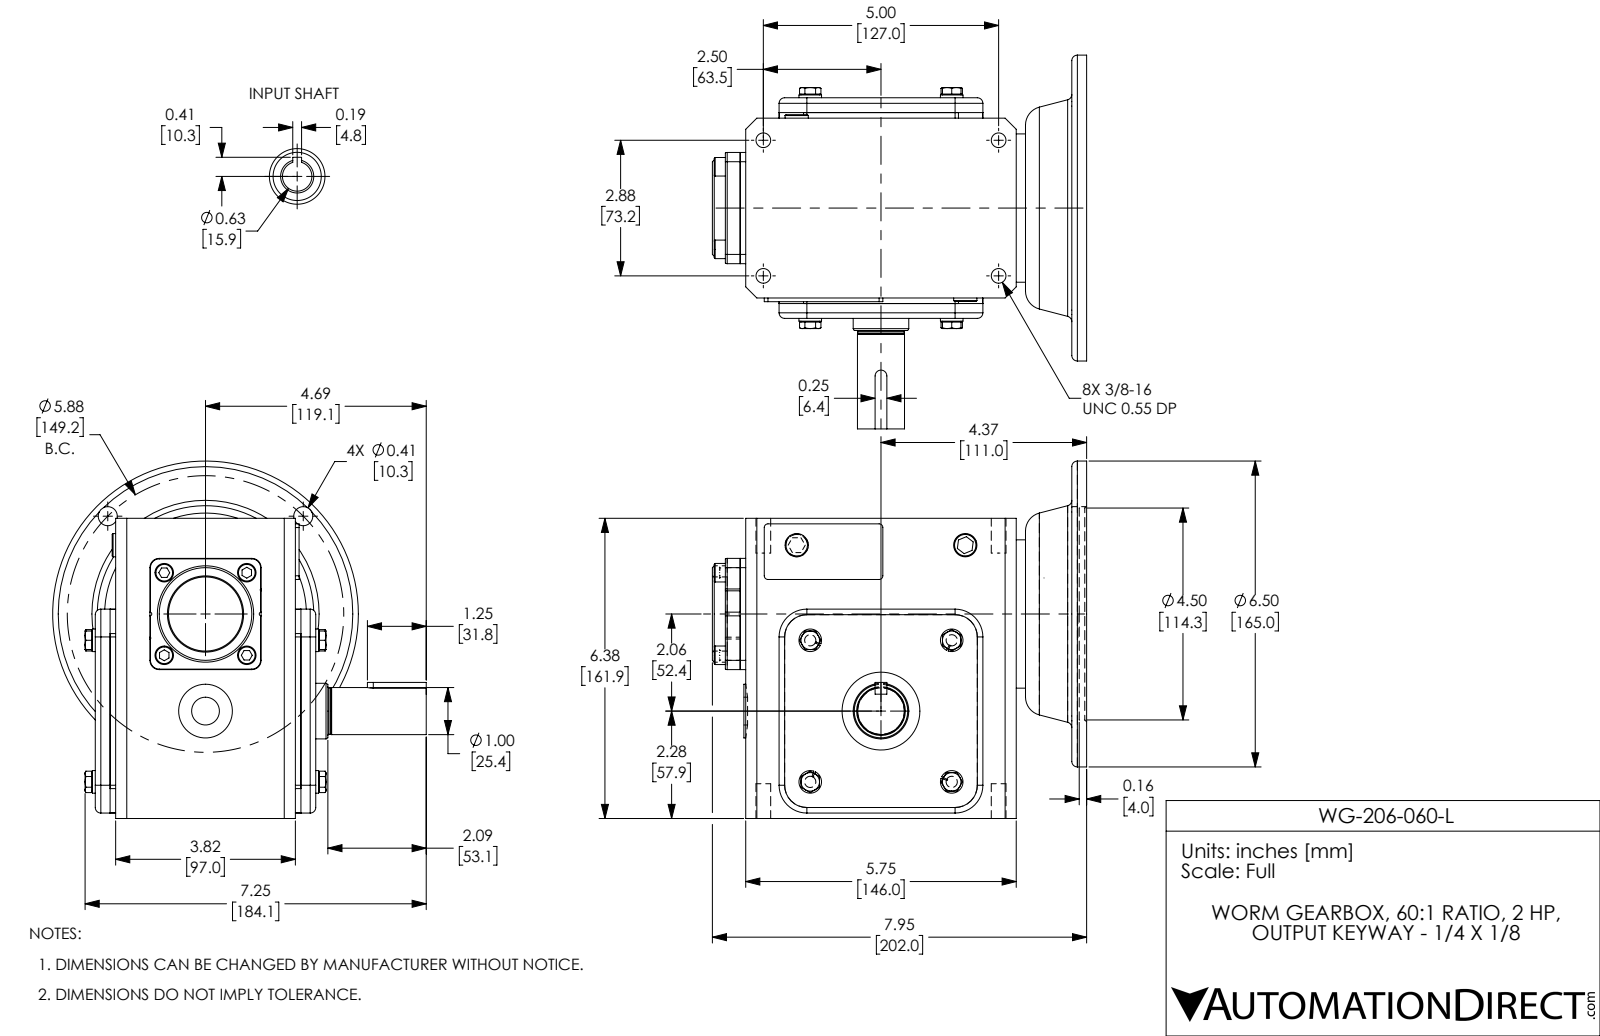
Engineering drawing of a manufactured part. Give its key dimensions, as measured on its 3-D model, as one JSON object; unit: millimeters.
{"part_name": "WG-206-060-L", "step_written_by": "SolidWorks 2017 (AUTOMOTIVE_DESIGN)", "units": "millimeters", "bodies": {"solids": 44, "faces": 619, "planar": 303, "cylindrical": 188, "other": 128}, "overall_size": [202, 201.6, 192.8], "volume_mm3": 2776000, "surface_area_mm2": 269800, "round_holes": [[8, 4], [10.3, 4], [12.6, 2], [30, 2], [15, 1], [15.9, 1], [37, 1], [42, 1], [90, 1], [114.3, 1]], "round_bosses_or_shafts": [[10, 8], [12.2, 4], [165, 1], [80, 1], [52, 1], [40, 1], [29, 1], [25.4, 1]], "partial_cylinders_radius": [[2, 8], [3, 8], [5, 4], [15, 4], [0.5, 2], [1, 2], [3.2, 1], [69, 1]], "face_to_face_distances": [8, 3, 103, 111, 11, 100, 108, 161.9, 119, 18], "hole_center_spacings": [74.6, 105.5, 52.8, 68.1, 73.2, 117.6, 127, 146.6]}
